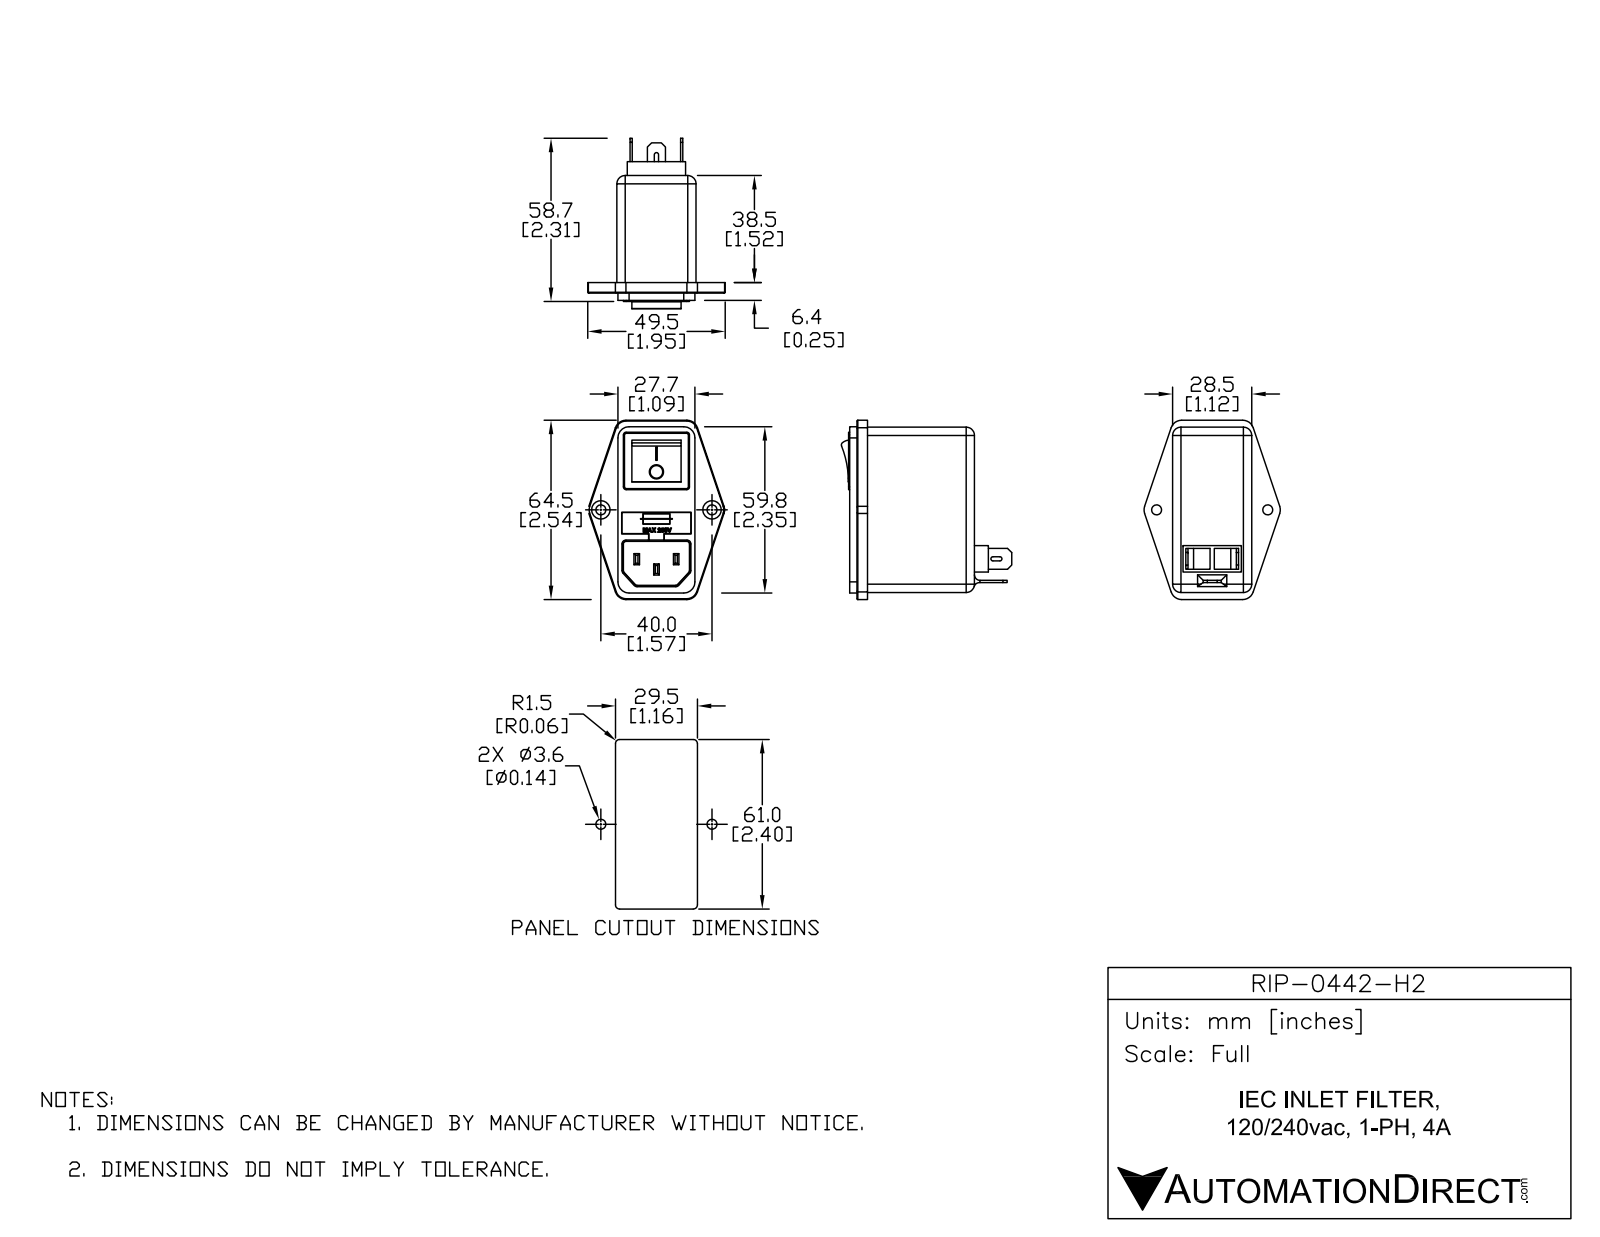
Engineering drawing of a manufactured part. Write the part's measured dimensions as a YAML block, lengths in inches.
part_name: "RIP0442H2"
step_written_by: "SolidWorks 2015 (AUTOMOTIVE_DESIGN)"
units: inches
bodies: {solids: 1, faces: 386, planar: 244, cylindrical: 87, other: 55}
overall_size: [2.539, 2.414, 1.935]
volume: 4.503
surface_area: 24.61
round_holes:
  - {diameter: 0.142, count: 2}
partial_cylinders:
  - {radius: 0.039, count: 11}
  - {radius: 0.157, count: 10}
  - {radius: 0.118, count: 8}
  - {radius: 0.016, count: 7}
  - {radius: 0.004, count: 6}
  - {radius: 0.079, count: 5}
  - {radius: 0.006, count: 4}
  - {radius: 0.024, count: 4}
face_to_face_distances: [1.122, 0.102, 2.343, 0.15, 0.252, 1.516, 1.768, 1.665, 0.098, 0.016]
hole_center_spacings: [1.575]
